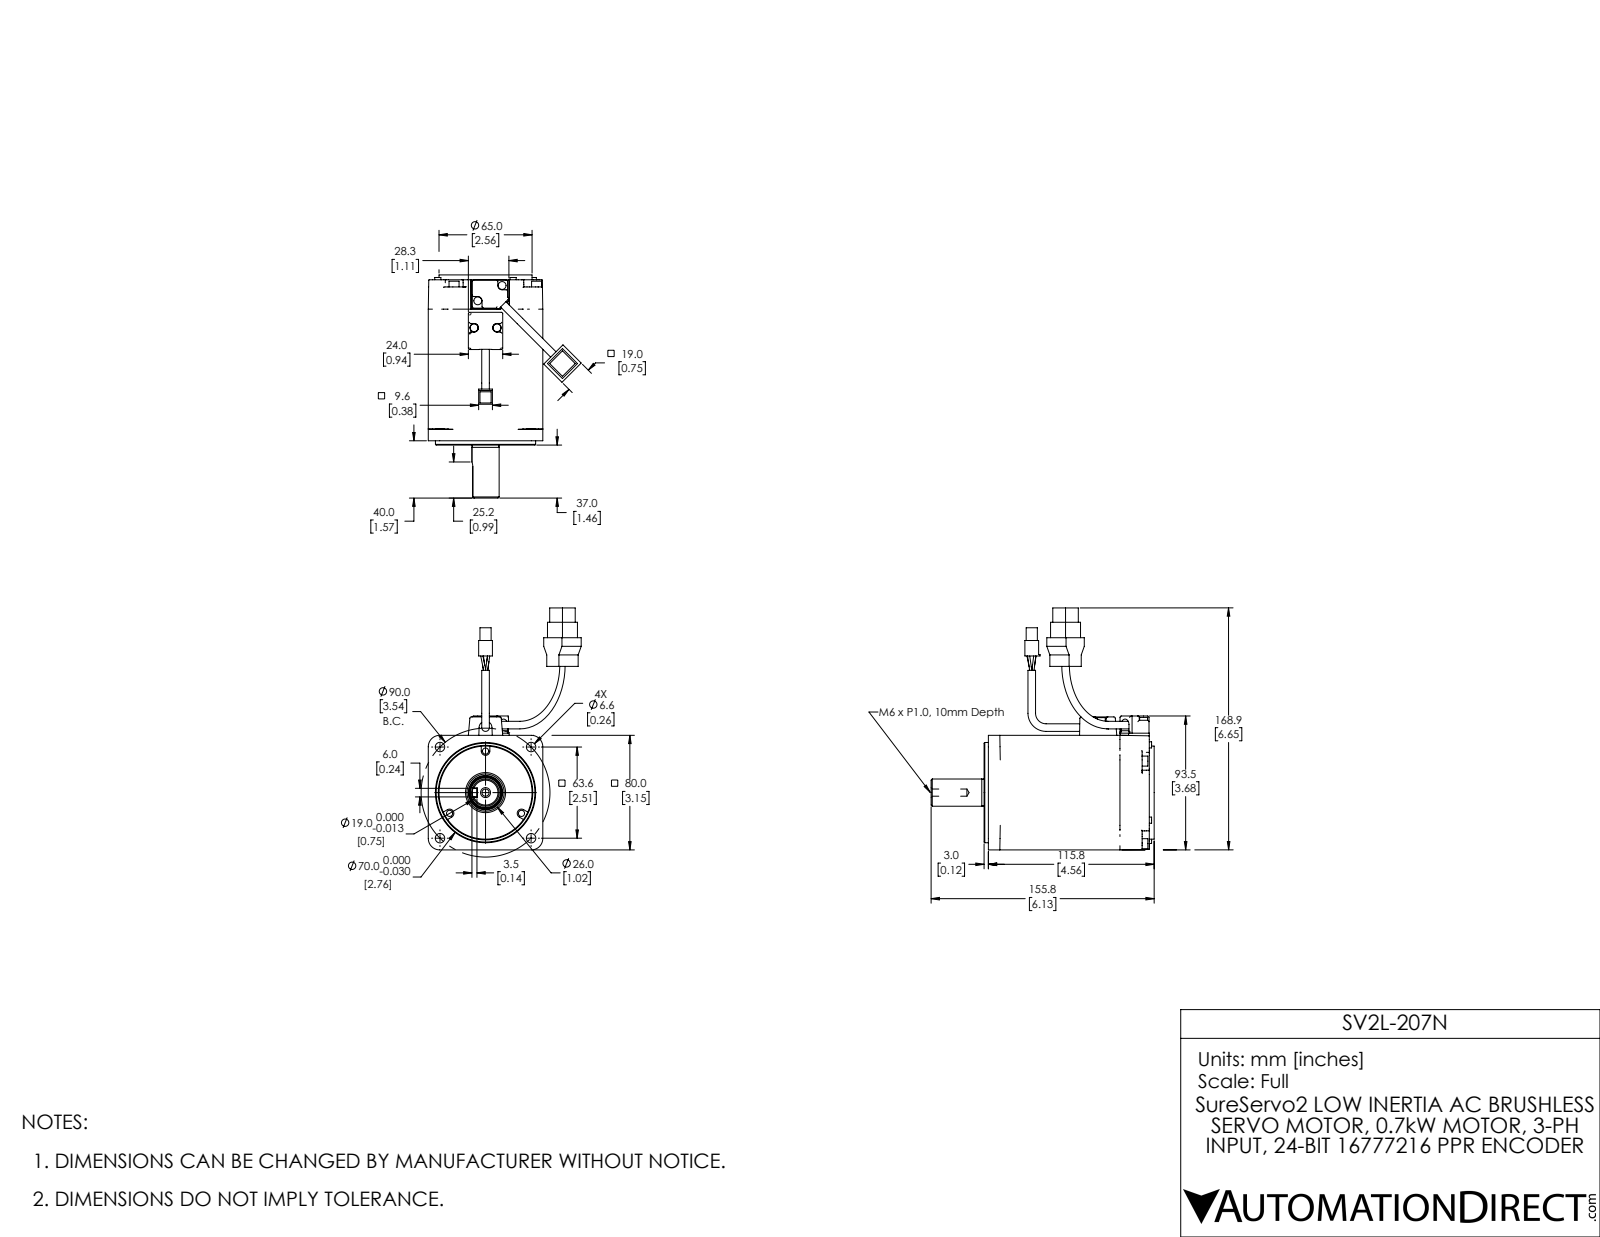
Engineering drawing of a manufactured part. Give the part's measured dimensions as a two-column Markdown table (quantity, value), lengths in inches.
| quantity | value |
| --- | --- |
| part name | ECM-A3H-CX0807RSX 2nd |
| STEP written by | SolidWorks 2017 (AUTOMOTIVE_DESIGN) |
| units | inches |
| bodies | 1 solid, 725 faces (223 planar, 294 cylindrical, 208 other) |
| overall size | 6.651 × 6.134 × 4.205 |
| volume | 42.24 in³ |
| surface area | 97.58 in² |
| round holes (diameter × count) | 0.26 × 4, 0.197 × 1, 0.236 × 1, 1.024 × 1, 1.102 × 1, 2.559 × 1 |
| round bosses / shafts (diameter × count) | 0.169 × 7, 0.276 × 4, 0.217 × 4, 0.209 × 4, 0.059 × 4, 0.228 × 2, 2.756 × 1, 0.945 × 1 |
| partial cylindrical surfaces (radius × count) | 0.039 × 46, 0.012 × 24, 0.118 × 22, 0.008 × 20, 0.079 × 16, 0.033 × 8, 0.072 × 8, 0.085 × 8 |
| main face-to-face distances | 3.15, 4.657, 4.559, 0.098, 0.138, 4.421, 4.52, 2.109, 0.118, 3.109 |
| hole center spacings | 1.772, 2.506, 3.543 |
